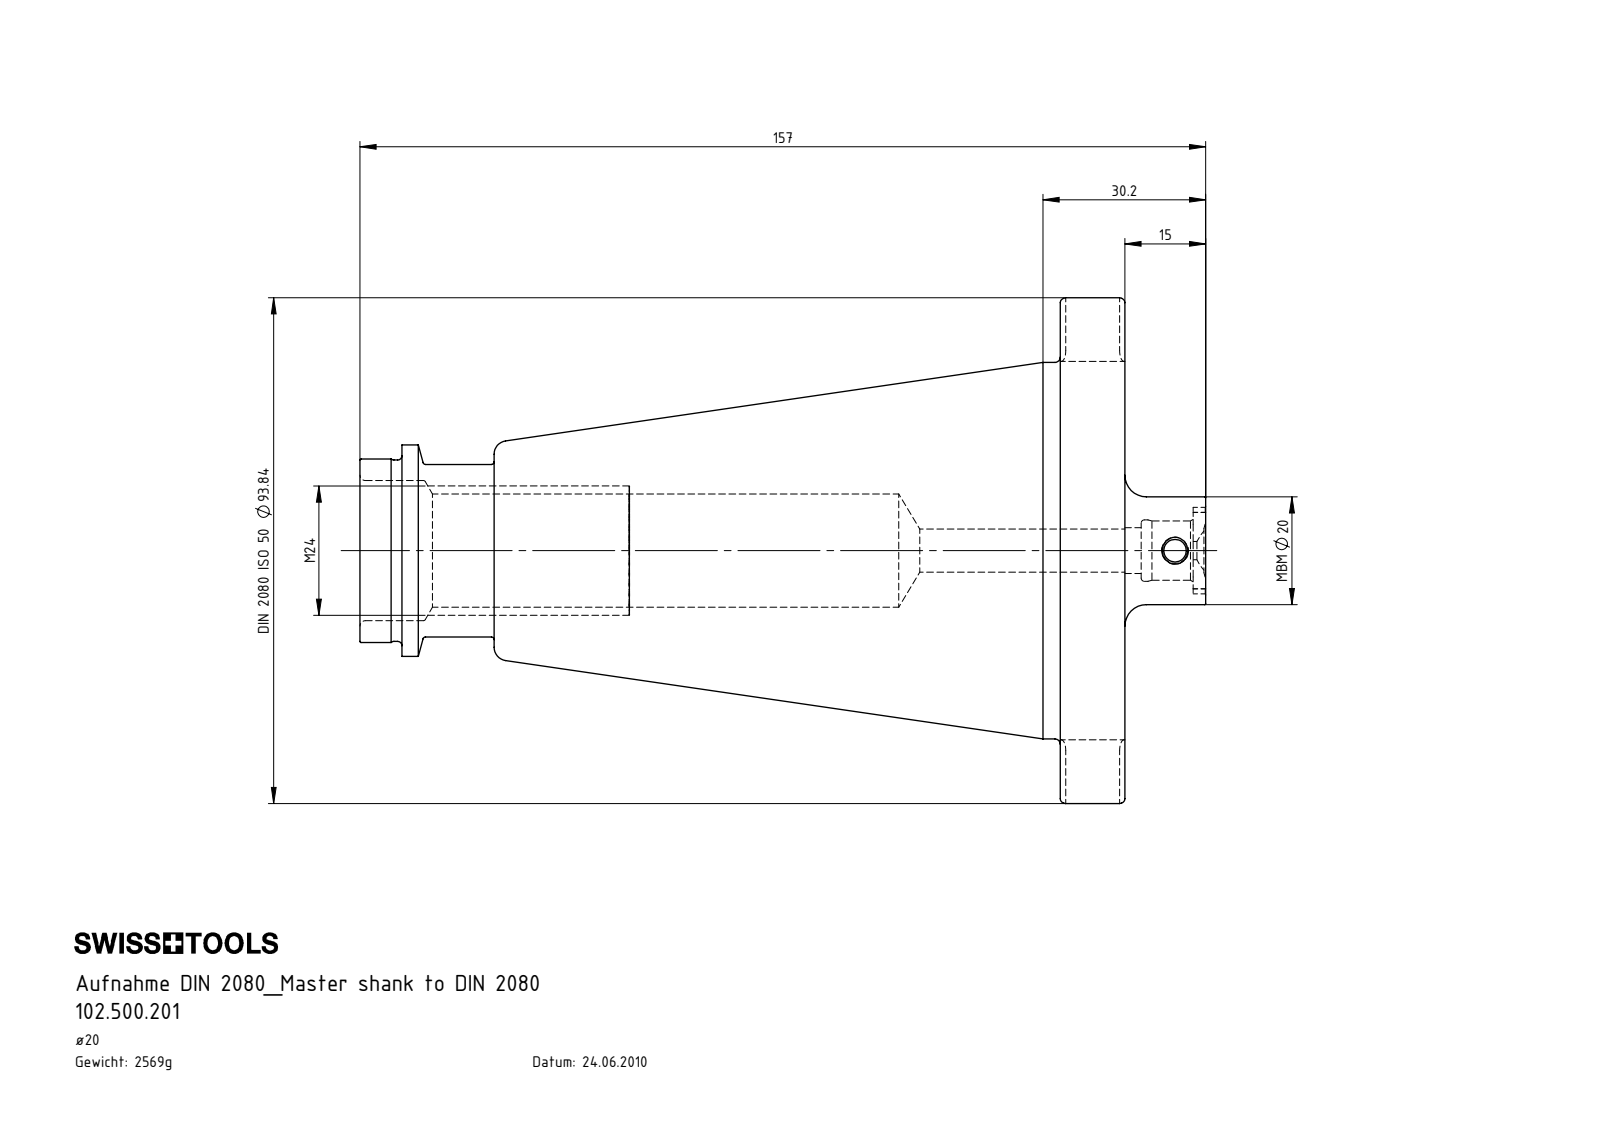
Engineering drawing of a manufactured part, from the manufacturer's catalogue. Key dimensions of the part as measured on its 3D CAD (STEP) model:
Part name (STEP PRODUCT): 102.500.201
STEP written by: SolidWorks 2017 (CONFIG_CONTROL_DESIGN)
Units: millimetres
Bodies: 1 solid, 134 faces (32 planar, 51 cylindrical, 51 other)
Overall size (bounding box): 157 × 97.3 × 93.84
Volume: 327 257 mm³ · Surface area: 45 567 mm²
Round holes (diameter × count): ⌀4.2 ×1, ⌀8 ×1, ⌀8.5 ×1, ⌀11 ×1, ⌀11.4 ×1, ⌀21 ×1, ⌀26 ×1
Round bosses / shafts (diameter × count): ⌀97.3 ×1, ⌀69.85 ×1, ⌀39.24 ×1, ⌀34.05 ×1, ⌀33.65 ×1, ⌀32 ×1, ⌀20 ×1
Partial cylindrical surfaces — rounded edges, fillets, slot ends (radius × count): R2 ×12, R2.2 ×4, R6.5 ×1, R8.03 ×1
Main face-to-face distances: 12, 130, 142, 70.2, 7.8, 122.2, 134.2, 25.7, 24.9, 17.1
